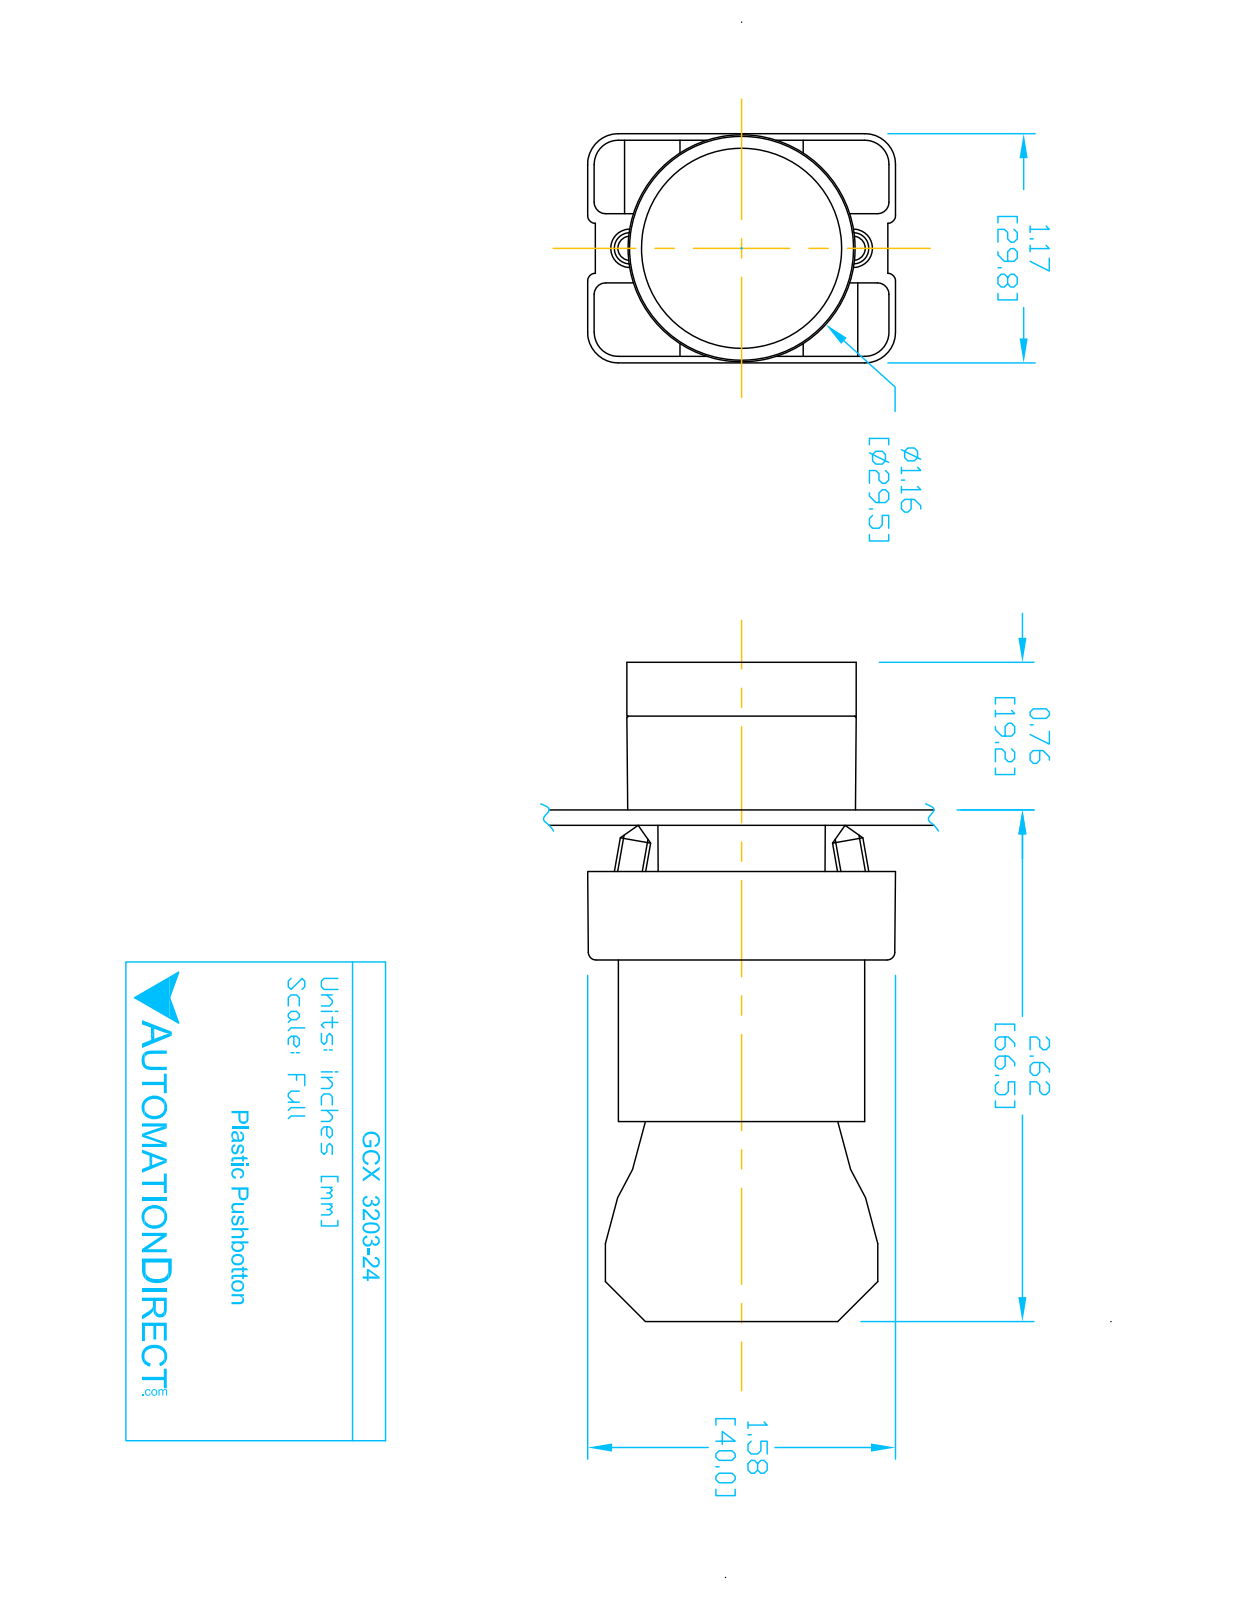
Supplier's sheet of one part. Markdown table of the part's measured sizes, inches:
| quantity | value |
| --- | --- |
| part name | ecx1040; ECX1050; GCX3203-24; ECX3029-2 (+1 more) |
| STEP written by | SolidWorks 2016 (AUTOMOTIVE_DESIGN) |
| units | inches |
| bodies | 8 solids, 431 faces (252 planar, 148 cylindrical, 31 other) |
| overall size | 3.319 × 1.581 × 1.177 |
| volume | 2.794 in³ |
| surface area | 38.77 in² |
| round holes (diameter × count) | 0.079 × 2, 0.124 × 2, 0.13 × 2, 0.087 × 1, 0.197 × 1, 0.469 × 1, 0.878 × 1, 0.888 × 1, 1.024 × 1 |
| round bosses / shafts (diameter × count) | 0.157 × 4, 1.175 × 1, 1.004 × 1, 0.945 × 1, 0.856 × 1, 0.78 × 1, 0.504 × 1 |
| partial cylindrical surfaces (radius × count) | 0.059 × 24, 0.041 × 12, 0.124 × 12, 0.157 × 12, 0.039 × 8, 0.128 × 2, 0.02 × 1, 0.063 × 1 |
| main face-to-face distances | 0.827, 0.579, 2.02, 1.193, 1.171, 0.276, 2.295, 1.469, 0.031, 0.033 |
| hole center spacings | 0.236, 0.544, 0.472, 0.49 |
